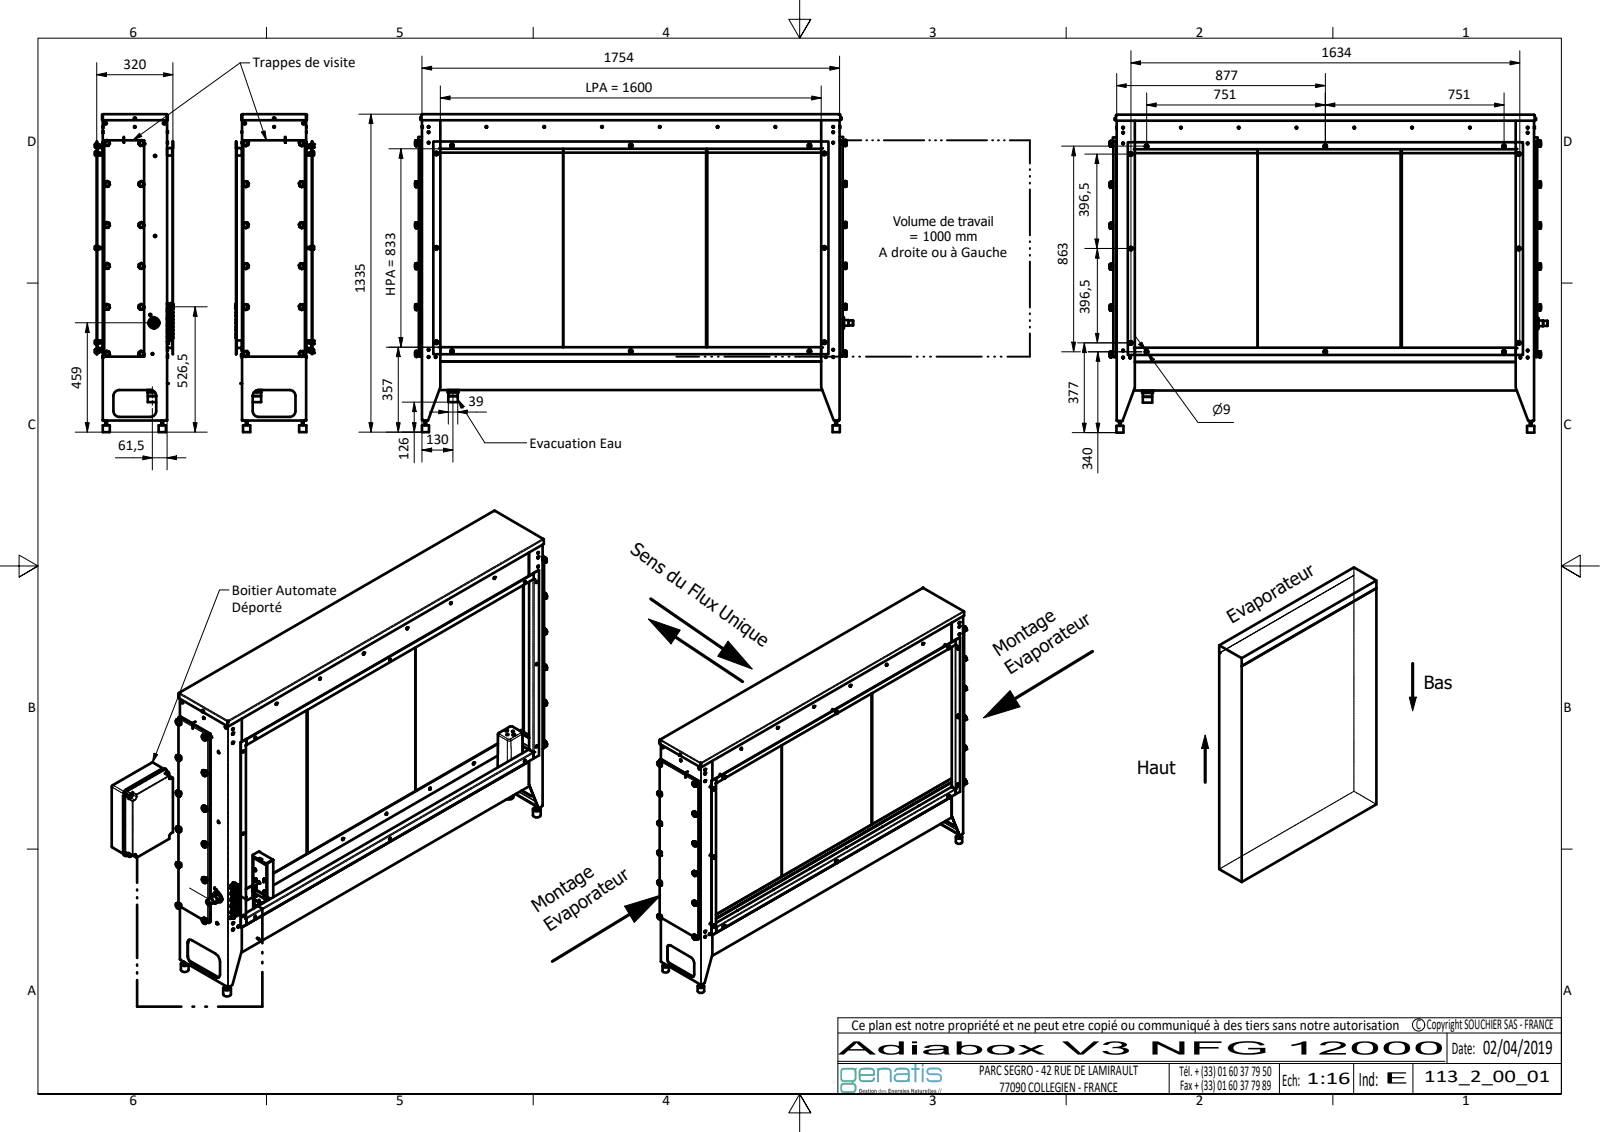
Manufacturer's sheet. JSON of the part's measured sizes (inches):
{"part_name": "113_2_00_01_-_Adiabox_V3; 113_2_00_06_-_Glissiere basse assemblee; 113_3_00_11_-_Cote gauche glissiere; 113_3_00_15_-_Tole de fond pliee (+8 more)", "step_written_by": "Autodesk Inventor 2022 (AUTOMOTIVE_DESIGN)", "units": "inches", "bodies": {"solids": 355, "faces": 9746, "planar": 4691, "cylindrical": 3039, "other": 2016}, "overall_size": [72.461, 52.559, 12.736], "volume_in3": 16384, "surface_area_in2": 31647, "round_holes": [[0.165, 67], [0.118, 59], [0.236, 57], [0.163, 52], [0.276, 22], [0.354, 15], [0.205, 13], [0.63, 9], [0.039, 8], [0.062, 8], [0.083, 8], [0.087, 8]], "round_bosses_or_shafts": [[0.311, 59], [0.157, 59], [0.433, 56], [0.197, 53], [0.276, 44], [0.335, 22], [0.079, 10], [0.906, 8]], "partial_cylinders_radius": [[0.118, 260], [0.315, 168], [0.059, 91], [0.004, 36], [0.012, 36], [0.039, 30], [0.02, 26], [0.492, 24]], "face_to_face_distances": [0.059, 3.937, 0.079, 10.433, 0.02, 10.492, 2.441, 0.531, 45.531, 43.091], "hole_center_spacings": [9.561, 19.122, 28.684, 38.245, 38.681, 42.077, 9.608, 47.197]}
